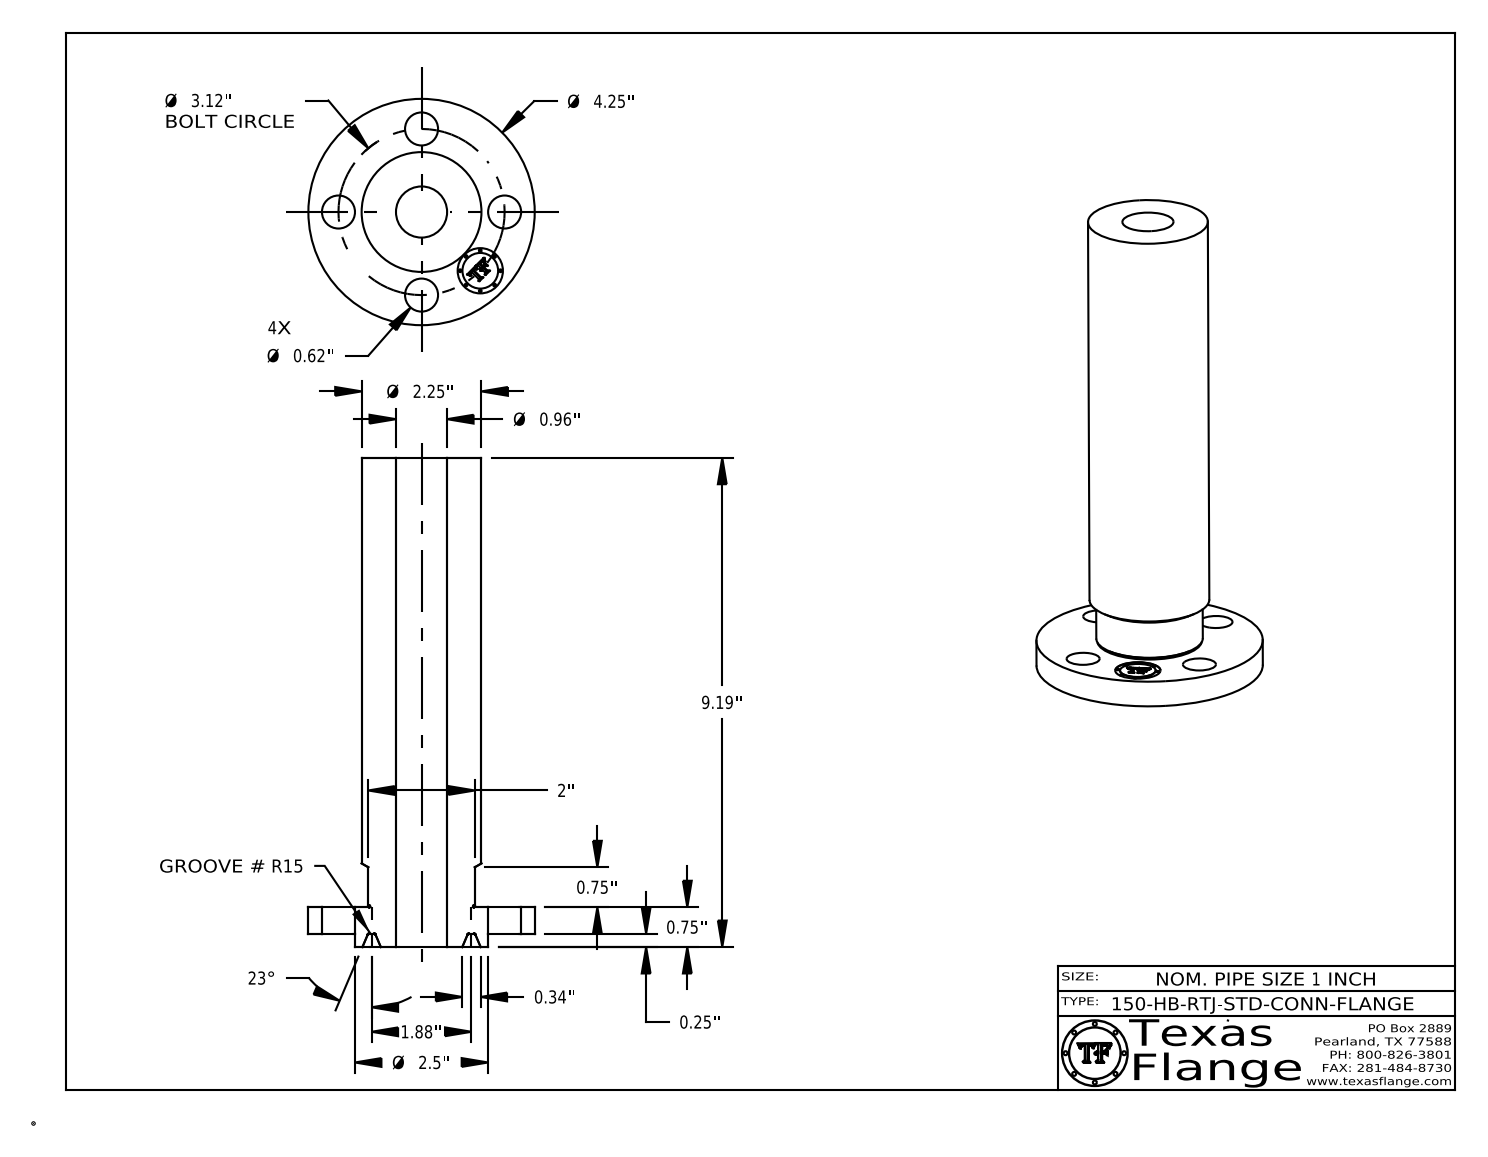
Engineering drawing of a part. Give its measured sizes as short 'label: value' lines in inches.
name: 1-150-HB-RTJ-STD-CONN-FLANGE
written by: CATIA V5 STEP AP214 (AUTOMOTIVE_DESIGN)
unit: in
bodies: 1 solid, 423 faces (371 planar, 38 cylindrical, 14 other)
size: 9.188 × 4.25 × 4.25
volume: 33.58 in³; area: 127.2 in²
holes: 4× ⌀0.62, 1× ⌀0.85, 1× ⌀0.96
bosses: 8× ⌀0.051, 1× ⌀4.25, 1× ⌀2.5, 1× ⌀2.25, 1× ⌀2, 1× ⌀0.67
face distances: 0.498, 8.937, 8.44, 0.25, 0.748, 9.187, 0.743, 0.493, 8.445, 0.254
hole spacings: 1.56, 2.206, 1.194, 2.882, 3.12, 1.56
